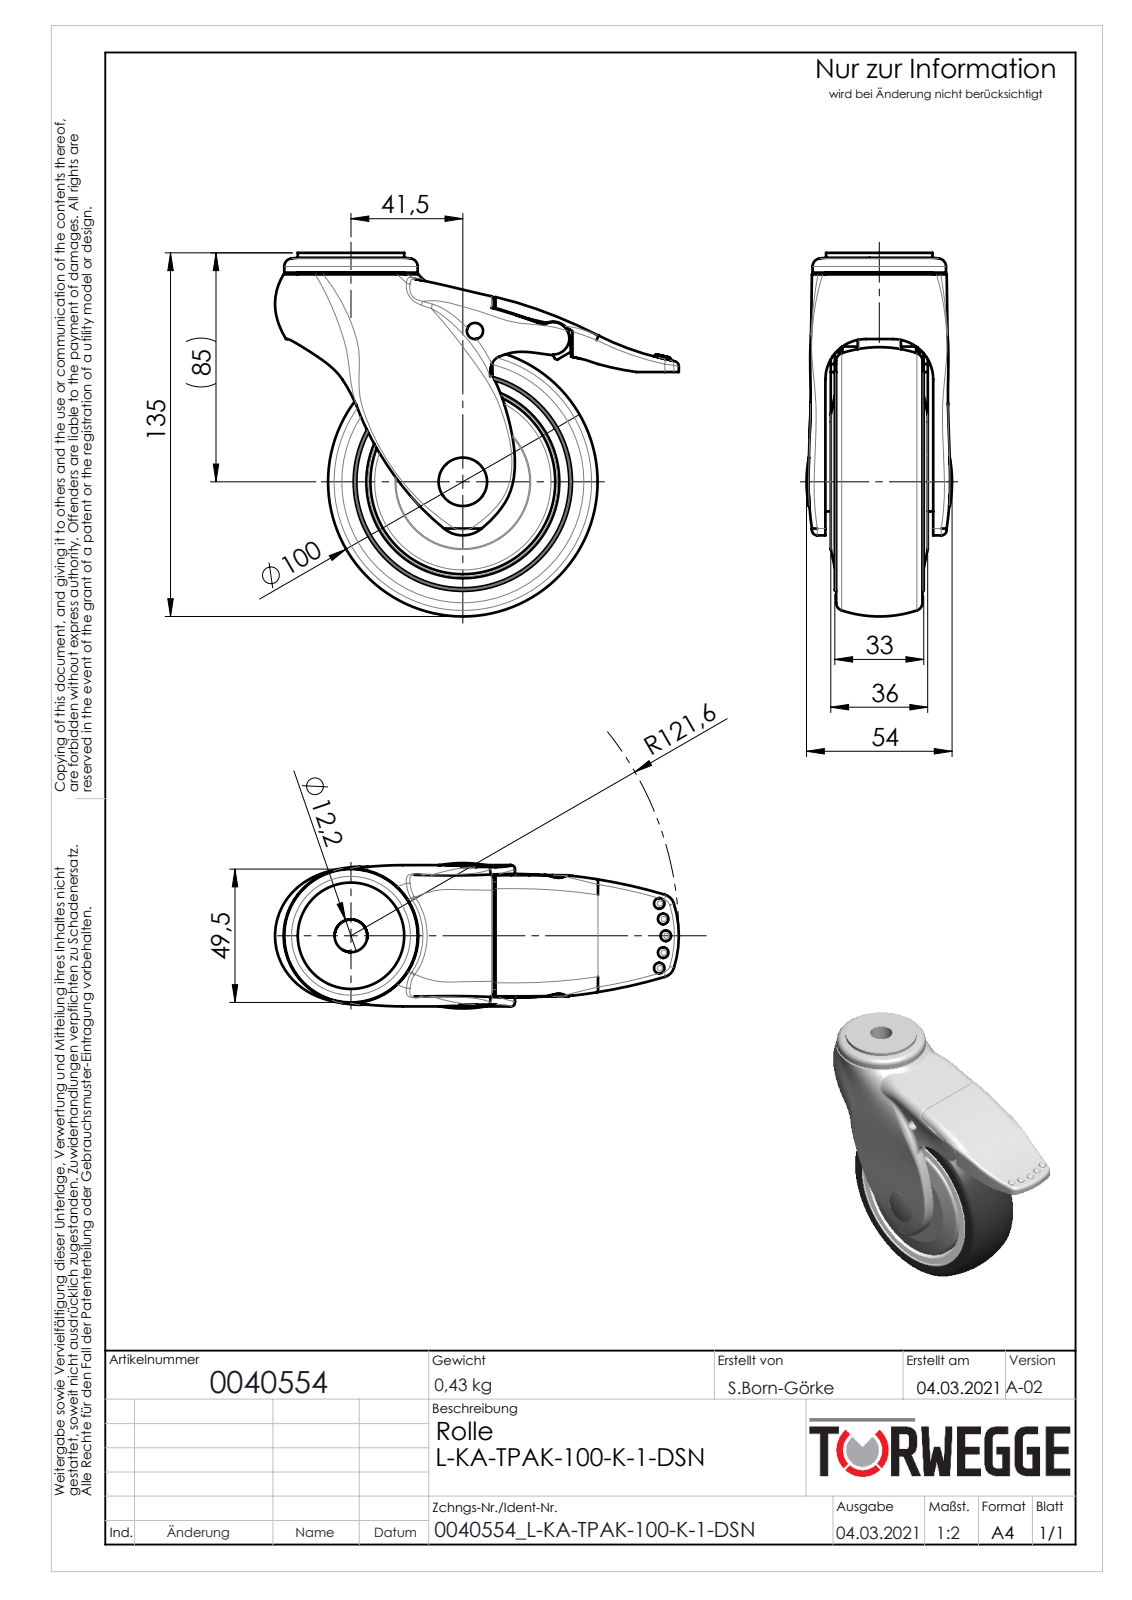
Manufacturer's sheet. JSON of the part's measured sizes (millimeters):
{"part_name": "0040554", "step_written_by": "SolidWorks 2020 (AUTOMOTIVE_DESIGN)", "units": "millimeters", "bodies": {"solids": 10, "faces": 632, "planar": 201, "cylindrical": 205, "other": 226}, "overall_size": [149.84, 135, 54], "volume_mm3": 283276, "surface_area_mm2": 106443, "round_holes": [[2, 3], [6, 1], [8.1, 1], [12.2, 1], [13, 1], [14, 1], [18, 1], [28.48, 1], [32, 1], [35, 1], [36.2, 1], [40, 1]], "round_bosses_or_shafts": [[1.95, 3], [81, 1], [68.6, 1], [49.5, 1], [39.5, 1], [34, 1], [22, 1], [21.52, 1]], "partial_cylinders_radius": [[2, 6], [0.5, 4], [1, 4], [5, 4], [15, 2], [200, 2], [3.05, 1], [6, 1]], "face_to_face_distances": [2, 36, 4, 34, 15.5, 32, 38, 18.5, 22.5, 17.5], "hole_center_spacings": [8, 13.86, 48.21, 56.18, 60.05, 61.08]}
